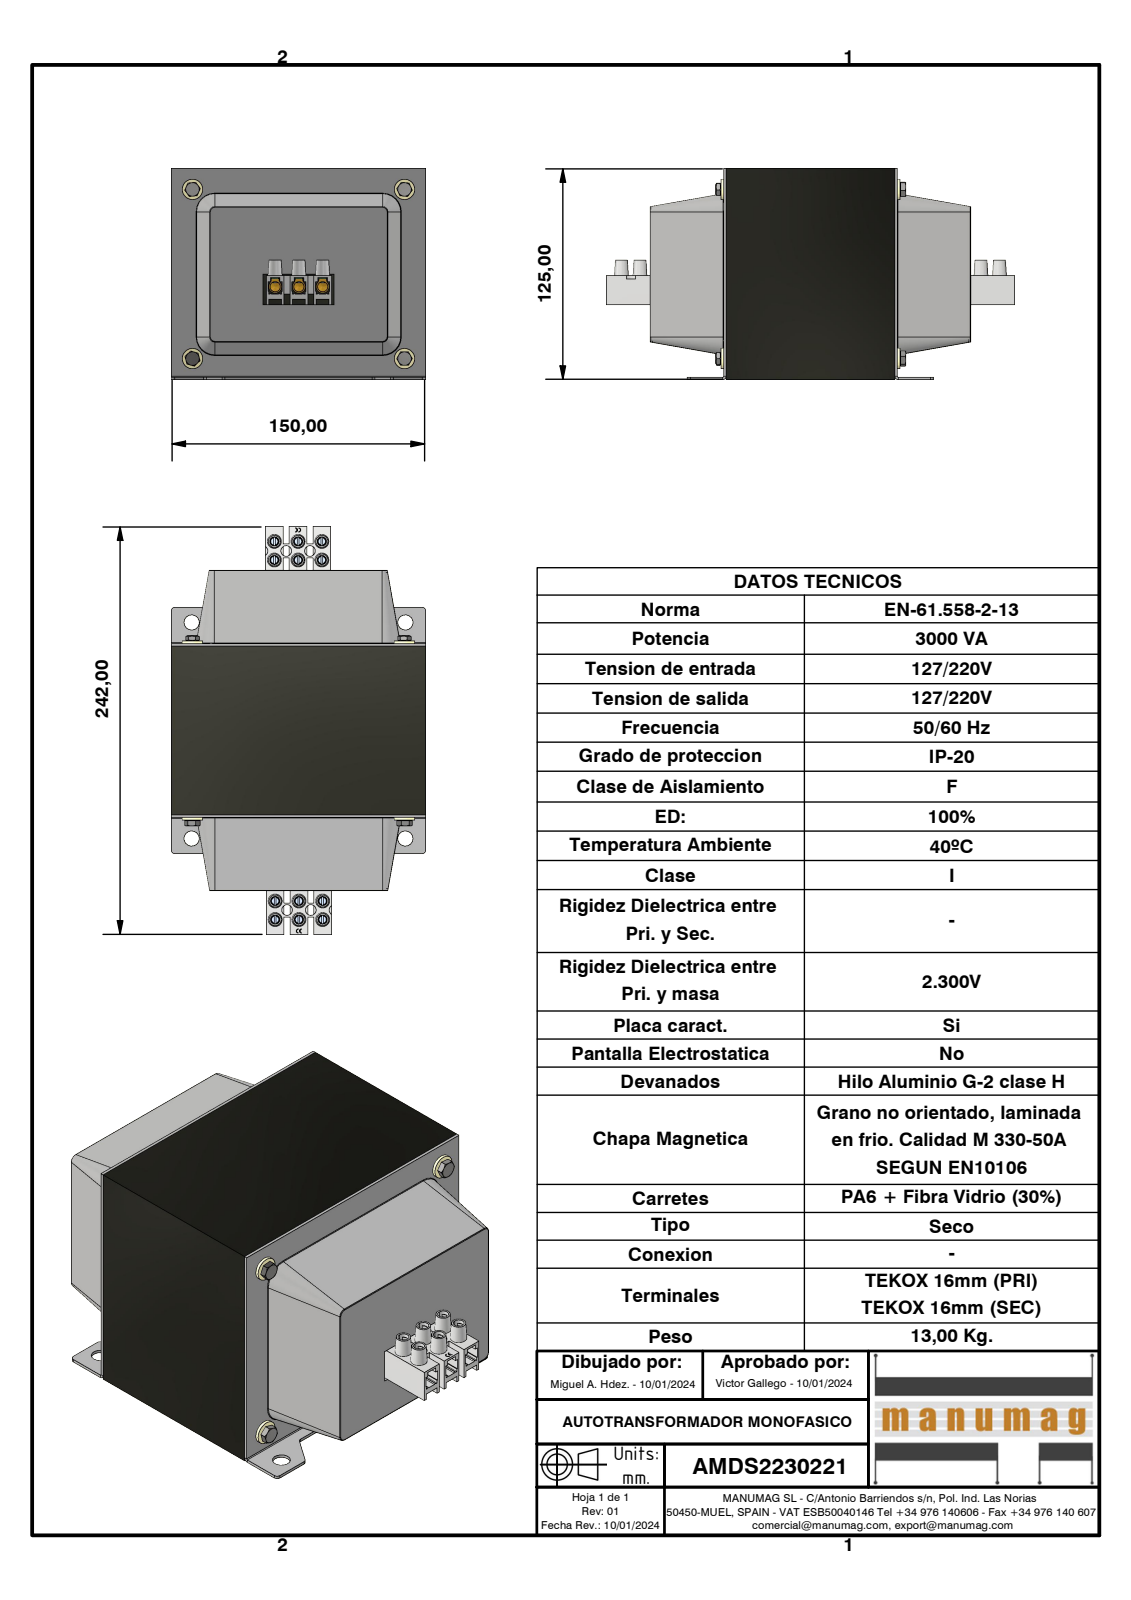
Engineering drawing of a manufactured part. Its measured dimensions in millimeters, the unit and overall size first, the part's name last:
Units: millimetres
Overall size (bounding box): 765.28 × 242 × 125
Round holes (diameter × count): ⌀3.24 ×16, ⌀5.5 ×12, ⌀6 ×10, ⌀5 ×4, ⌀6.3 ×4, ⌀8 ×4, ⌀9 ×4
Round bosses / shafts (diameter × count): ⌀4 ×12, ⌀12 ×4, ⌀6.7 ×4, ⌀5.9 ×4, ⌀4.57 ×4
Partial cylindrical surfaces — rounded edges, fillets, slot ends (radius × count): R2.75 ×24, R0.38 ×16, R0.82 ×16, R2 ×14, R3 ×12, R0.81 ×8, R0.1 ×6, R0.22 ×6
Main face-to-face distances: 100, 25, 1.5, 125, 145, 43.5, 50, 75, 45, 143.5
Hole centre spacings: 14, 8.8, 9, 17.8, 11, 28, 213, 21.67
Volume: 1 567 000 mm³ · Surface area: 313 381 mm²
Bodies: 51 solids, 2194 faces (1488 planar, 286 cylindrical, 420 other)
Part name (STEP PRODUCT): AMDS2230221; centrador M5; DIN 934 - M4 x 0,7; TAPA RC50 VENTANA 3 ELEMENTOS 16 CON FICHAS (+8 more)
STEP written by: Autodesk Inventor 2023 (AUTOMOTIVE_DESIGN)
